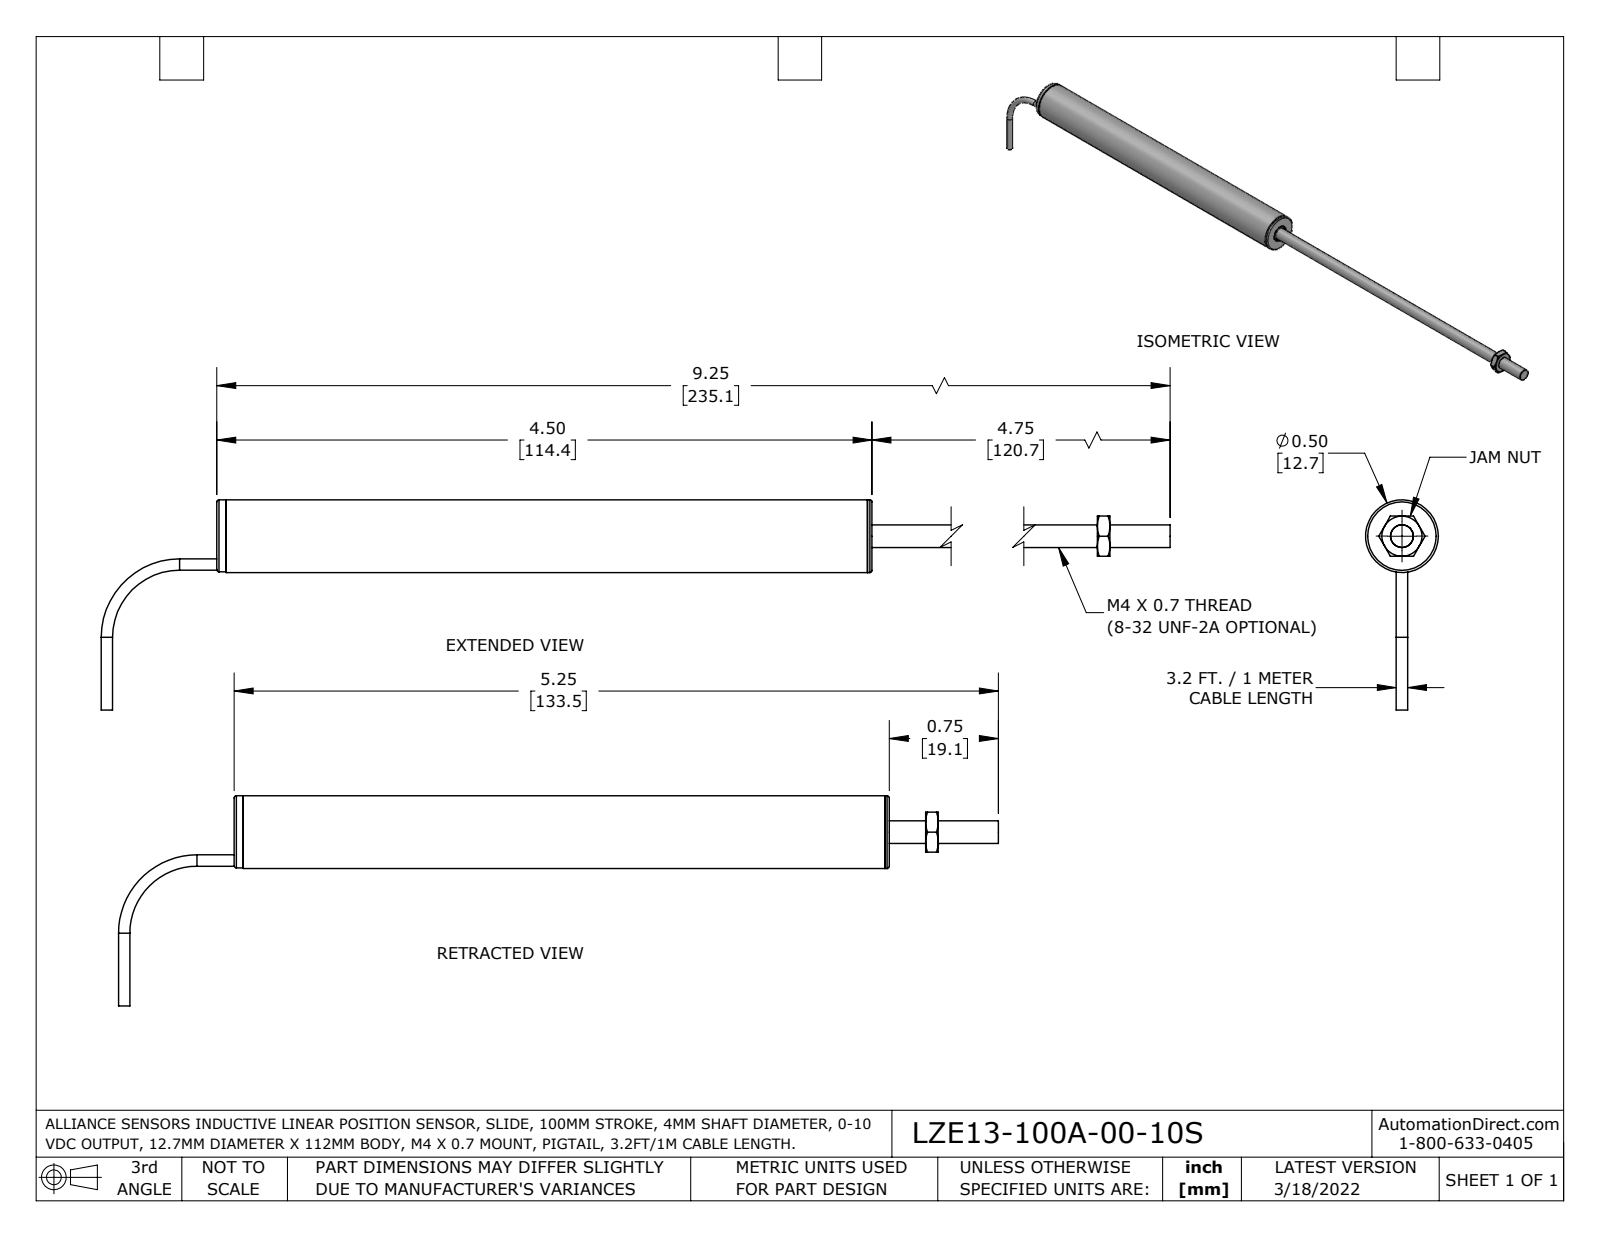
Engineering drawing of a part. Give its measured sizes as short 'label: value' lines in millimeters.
name: 5300-0002; 3120-0040_SHRINK; 3120-0033-XX_3120-0033-04; 3120-0034-XX-Z_3120-0034-04-Z (+6 more)
written by: SolidWorks 2021 (AUTOMOTIVE_DESIGN)
unit: mm
bodies: 9 solids, 98 faces (32 planar, 38 cylindrical, 28 other)
size: 255.2 × 36.7 × 12.7
volume: 5 160 mm³; area: 15 730 mm²
holes: 1× ⌀2, 1× ⌀4, 1× ⌀4.7, 1× ⌀5.7
bosses: 1× ⌀12.7, 1× ⌀11.9, 1× ⌀5.6, 1× ⌀4, 1× ⌀2.5, 1× ⌀2
rounds: 1× R1.2
face distances: 2, 1.6, 7, 2.4, 114.4, 112.8, 112, 110.4, 0.8, 108
hole spacings: 5
